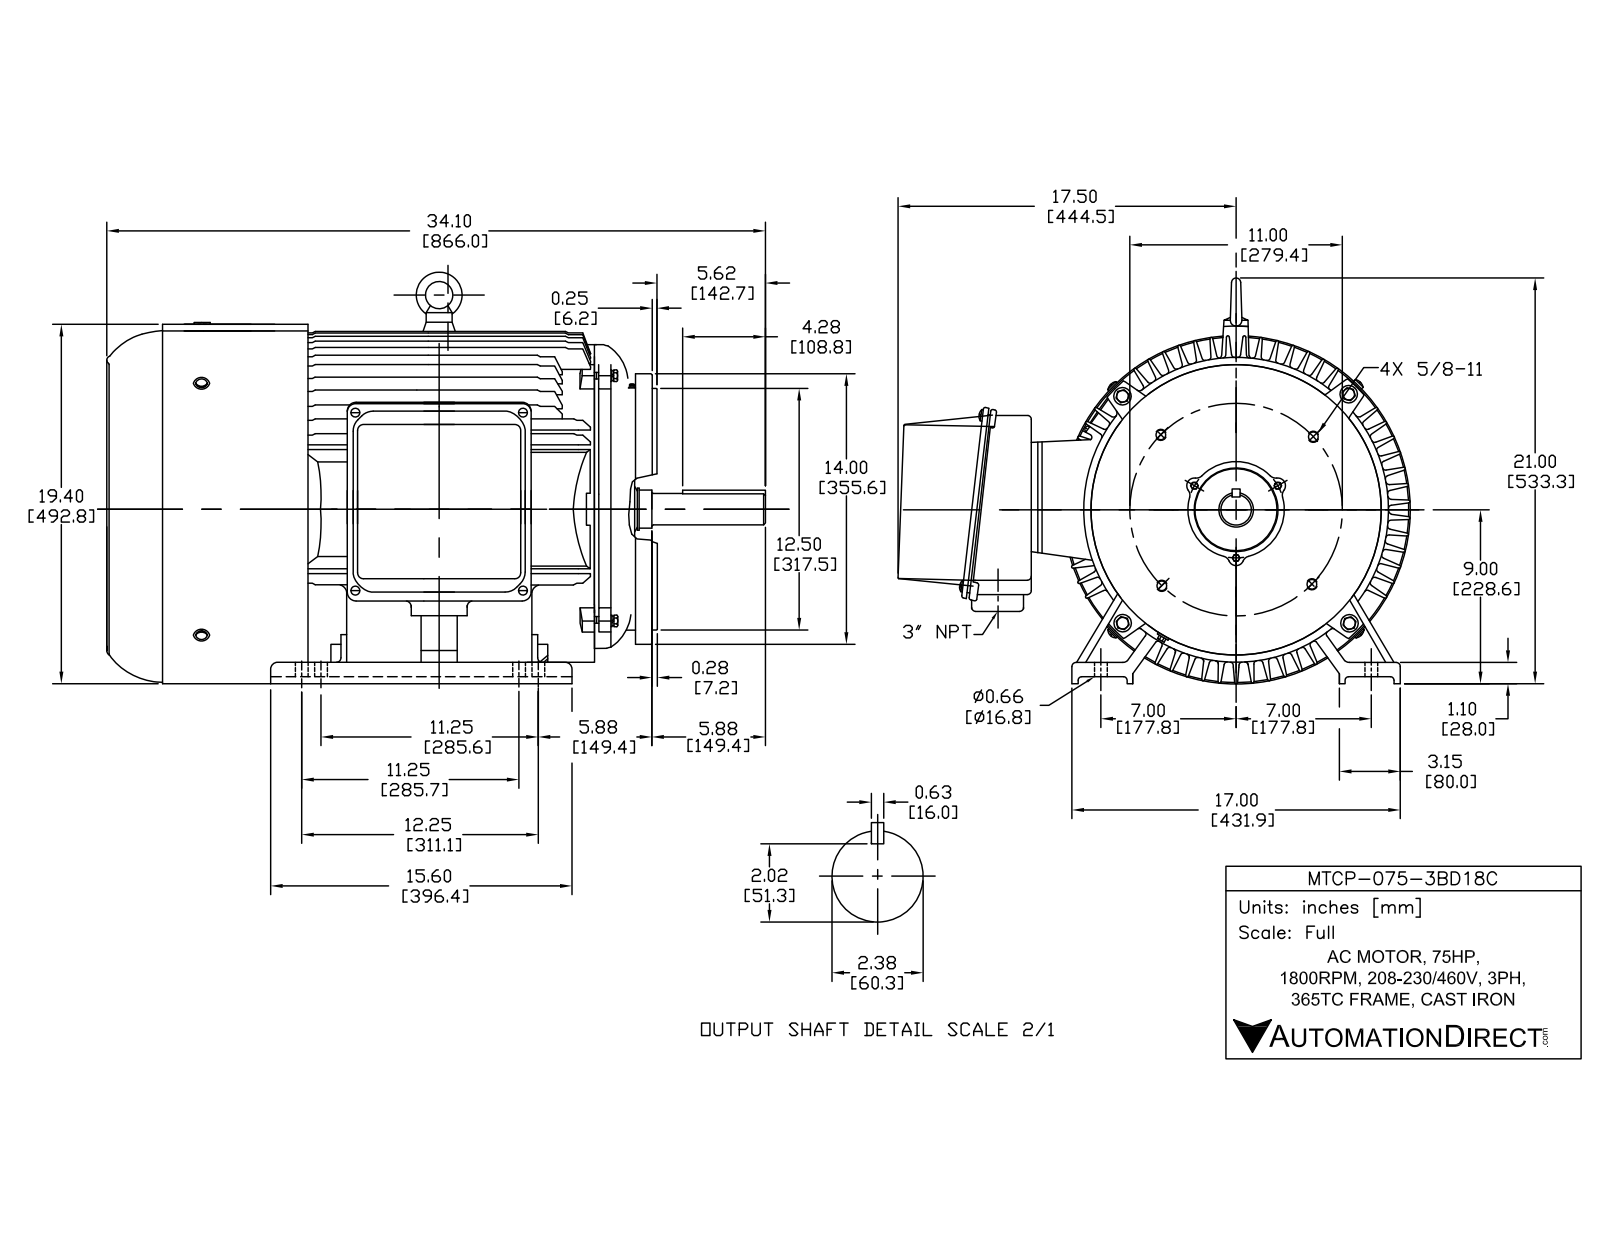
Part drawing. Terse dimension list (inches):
name: 橡皮塞17; PE360接线盒座_默认_按加工; spring lock washers--normal type gb_GB_FASTENER_WASHER_SW 6; hex head bolts-full thread grade c gb_GB_FASTENER_BOLT_HHBFTC M8X20-N (+8 more)
written by: SolidWorks 2017 (AUTOMOTIVE_DESIGN)
unit: in
bodies: 64 solids, 4257 faces (1035 planar, 1572 cylindrical, 1650 other)
size: 34.311 × 26.456 × 21.37
volume: 1 315 in³; area: 7 789 in²
holes: 19× ⌀0.394, 10× ⌀0.268, 10× ⌀0.531, 8× ⌀0.669, 5× ⌀0.472, 4× ⌀0.197, 4× ⌀0.236, 4× ⌀0.252, 4× ⌀0.263, 4× ⌀0.402, 4× ⌀0.508, 4× ⌀0.512
bosses: 8× ⌀0.472, 8× ⌀0.315, 4× ⌀0.945, 4× ⌀0.752, 4× ⌀0.394, 4× ⌀0.389, 4× ⌀0.236, 1× ⌀18.937
rounds: 207× R0.039, 156× R0.197, 121× R0.079, 83× R0.02, 39× R0.059, 24× R0.236, 20× R0.472, 15× R0.157
face distances: 0.236, 0.059, 1.004, 0.256, 1.123, 8.898, 0.079, 1.102, 0.197, 0.315
hole spacings: 5.118, 4.209, 5.5, 6.31, 10.163, 10.427, 13.328, 2.953
